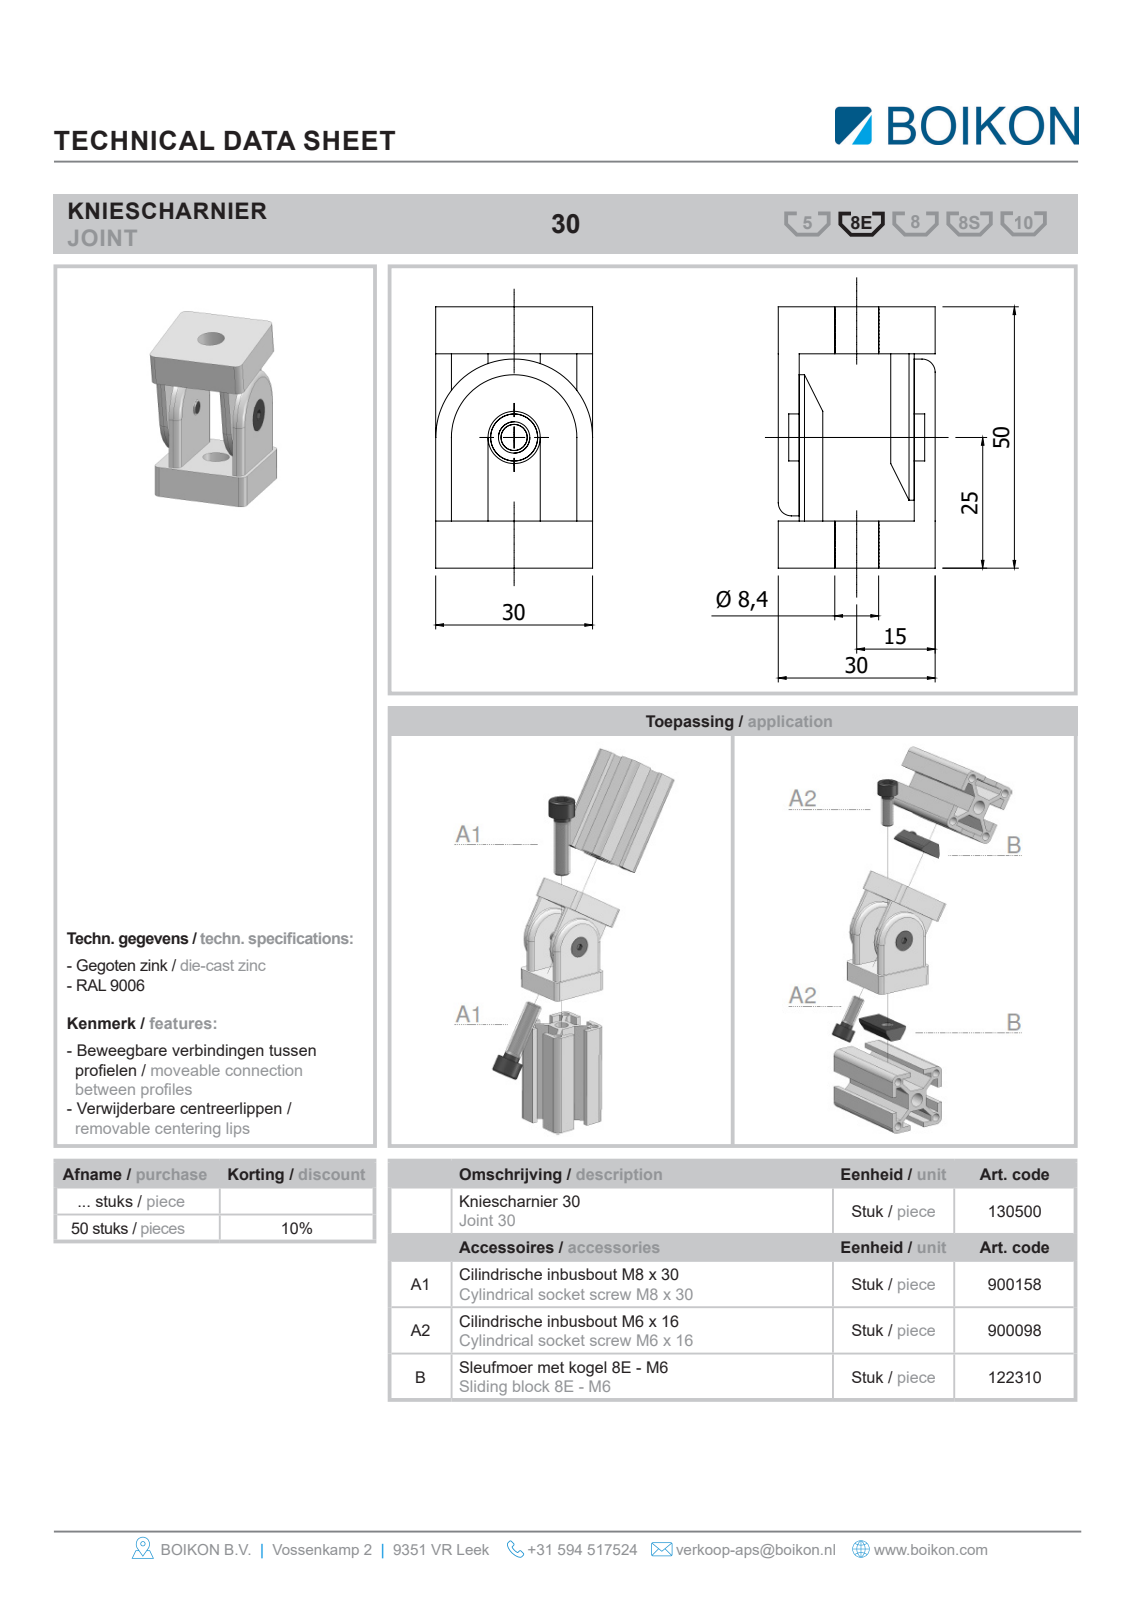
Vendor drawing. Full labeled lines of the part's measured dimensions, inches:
Part name (STEP PRODUCT): Root; 130500Scharnier 30BOIKON; ISO 10642-M5x8-8.8Countersunk head bolts0
STEP written by: HiCAD 2013 1802.4 Build 509 (AUTOMOTIVE_DESIGN)
Units: inches
Bodies: 4 solids, 114 faces (60 planar, 44 cylindrical, 10 other)
Overall size (bounding box): 1.969 × 1.181 × 1.181
Volume: 1.573 in³ · Surface area: 20.5 in²
Round holes (diameter × count): ⌀0.163 ×1, ⌀0.217 ×1, ⌀0.327 ×1, ⌀0.866 ×1
Round bosses / shafts (diameter × count): ⌀1.102 ×1, ⌀0.551 ×1, ⌀0.394 ×1, ⌀0.295 ×1, ⌀0.197 ×1, ⌀0.158 ×1
Partial cylindrical surfaces — rounded edges, fillets, slot ends (radius × count): R0.079 ×12, R0.217 ×1
Main face-to-face distances: 0.972, 0.039, 0.169, 0.02, 0.374, 1.594, 0.157, 0.685, 0.13, 0.287
